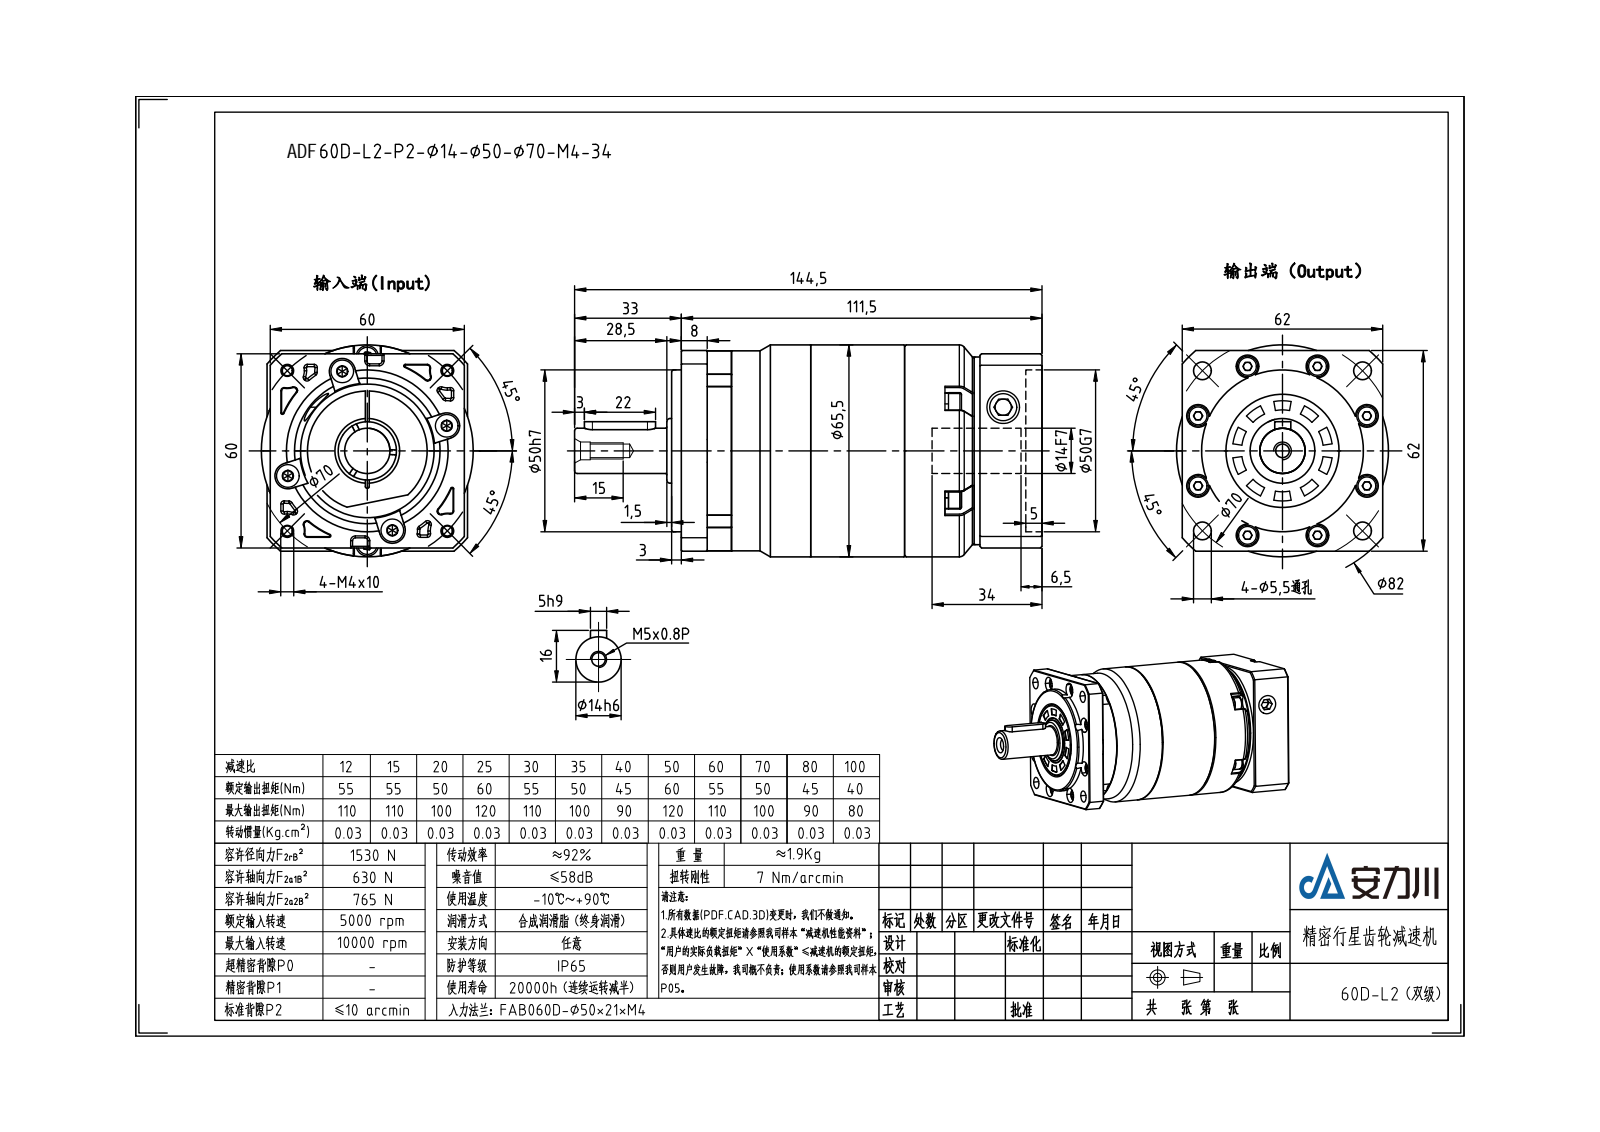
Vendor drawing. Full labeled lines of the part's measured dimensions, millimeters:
Part name (STEP PRODUCT): FGA060D-L2-14-50-70-M5-341; A型平键5-22; FAB060D输出行星架-14轴; hex socket set screws with cone point gb_GB_FASTENER_SCREWS_HSCP M10X10-N (+8 more)
STEP written by: SolidWorks 2014 (AUTOMOTIVE_DESIGN)
Units: millimetres
Bodies: 30 solids, 1430 faces (512 planar, 386 cylindrical, 532 other)
Overall size (bounding box): 144.5 × 65.5 × 65.5
Volume: 349 186 mm³ · Surface area: 89 979 mm²
Round holes (diameter × count): ⌀3.3 ×16, ⌀4.5 ×10, ⌀5.5 ×6, ⌀4.2 ×1, ⌀4.3 ×1, ⌀8.5 ×1, ⌀9 ×1, ⌀14 ×1, ⌀14.5 ×1, ⌀31.86 ×1, ⌀35 ×1, ⌀38 ×1
Round bosses / shafts (diameter × count): ⌀7 ×10, ⌀4 ×10, ⌀5.5 ×8, ⌀3 ×8, ⌀65.5 ×1, ⌀61.8 ×1, ⌀58 ×1, ⌀51.5 ×1
Partial cylindrical surfaces — rounded edges, fillets, slot ends (radius × count): R0.3 ×56, R0.5 ×12, R4 ×10, R1 ×8, R5 ×4, R37.5 ×3, R0.4 ×2, R2.5 ×2
Main face-to-face distances: 21.5, 29, 50.5, 24.5, 53.5, 3, 18.5, 72, 75, 61
Hole centre spacings: 29, 14.01, 21.62, 28.25, 35.59, 39.95, 52.2, 52.73
